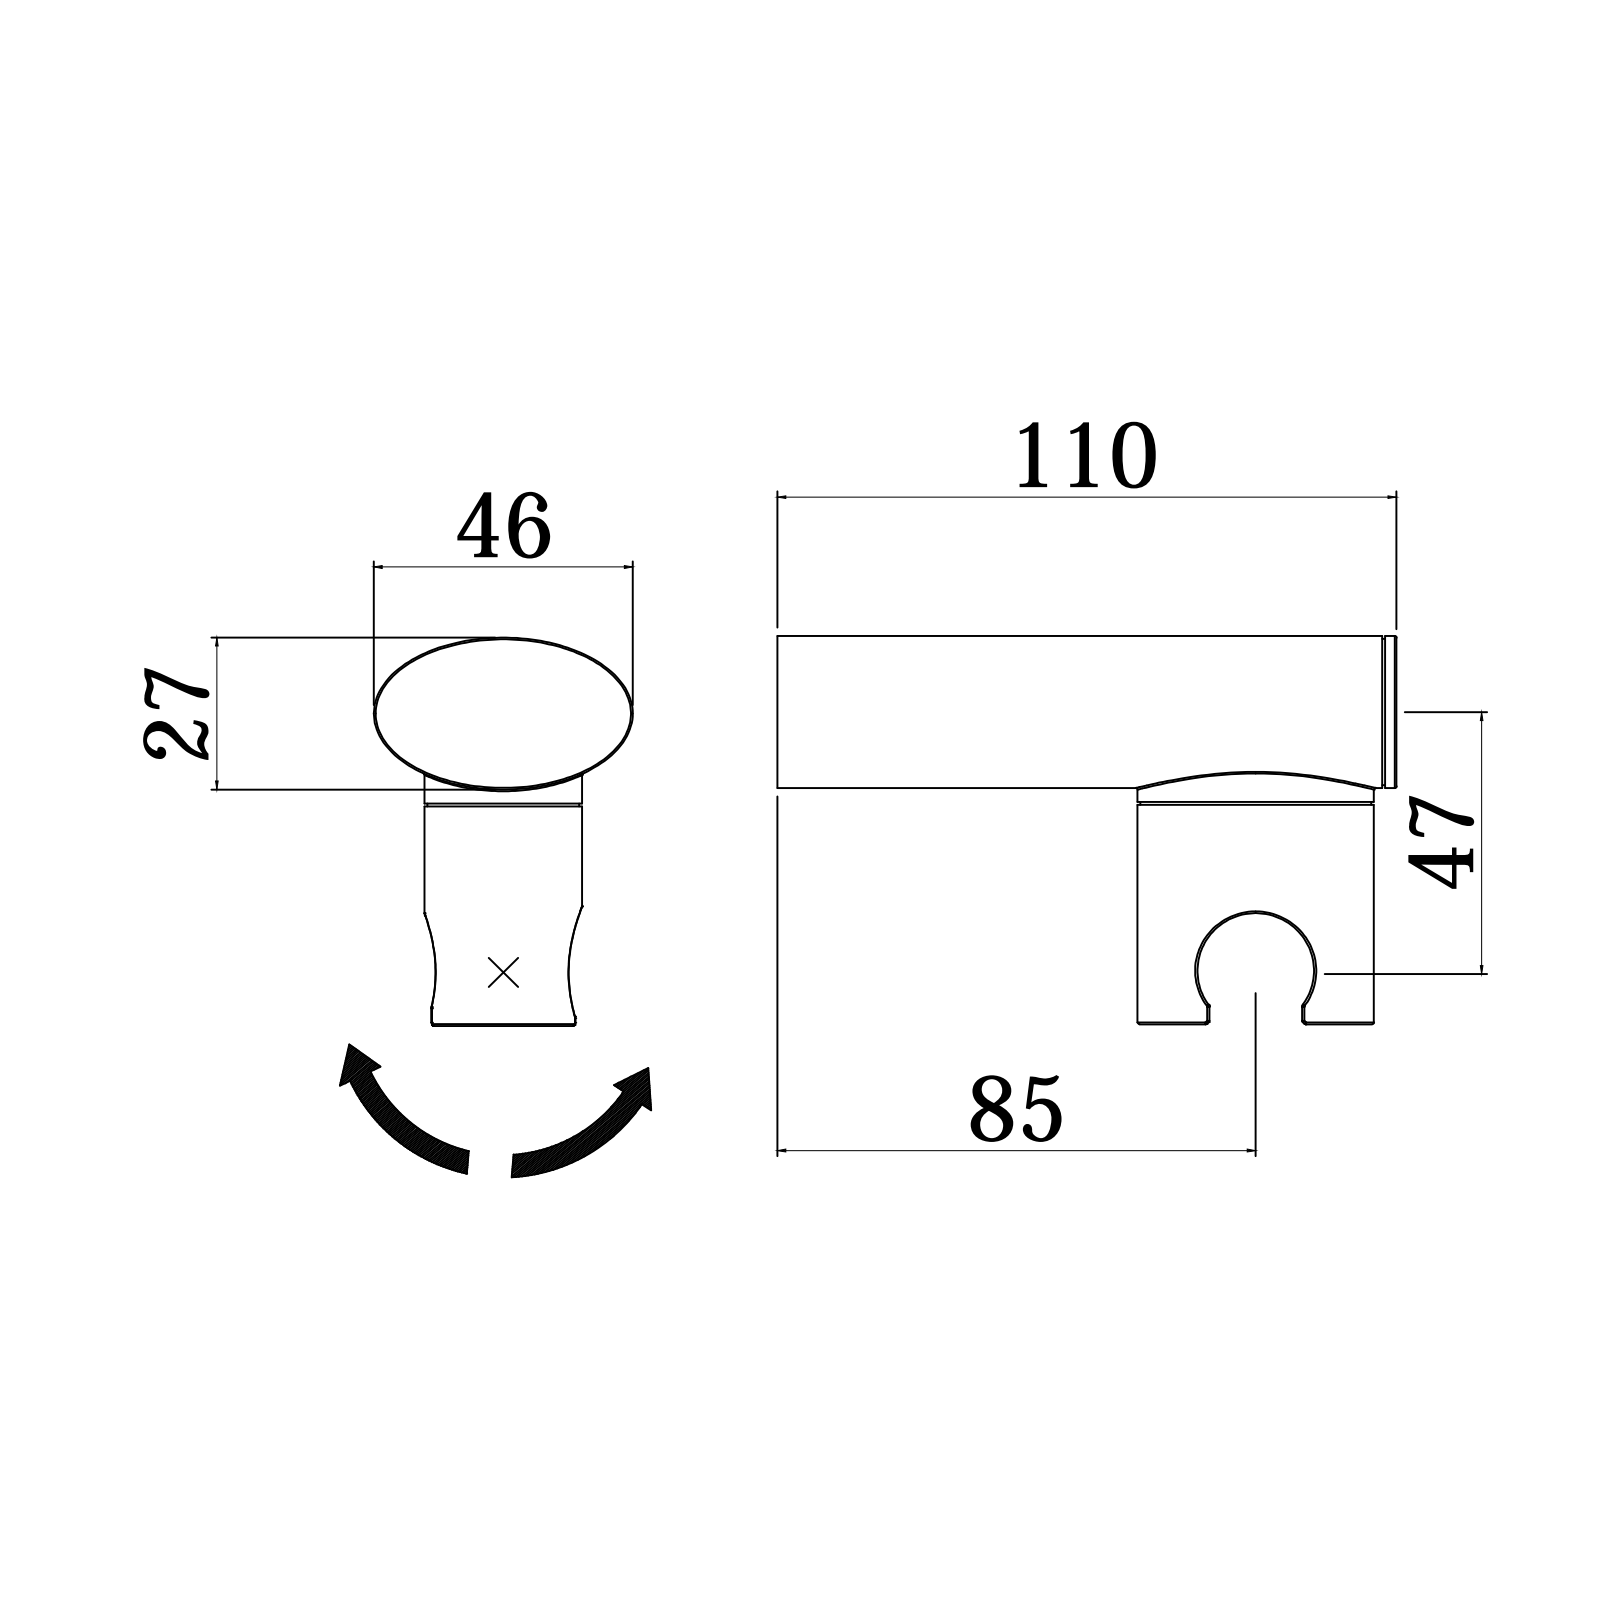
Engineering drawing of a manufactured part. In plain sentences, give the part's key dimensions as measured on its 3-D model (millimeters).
The part is named "4071431CR_CORPO; 4071431CR_PLACCHETTA; 4071431CR_GANCIO; 4071431CR_VITE (+1 more)". Its 3-D file was written by "CREO PARAMETRIC BY PTC INC, 2020044 (CONFIG_CONTROL_DESIGN)". It is 2 solids with 821 faces: 225 planar, 194 cylindrical and 402 other. Overall it measures 111 by 68.91 by 46 millimeters. Its volume is 2 818 cubic millimeters and its surface area 44 492 square millimeters. Round bosses or shafts: 1 of diameter 7.4, 1 of diameter 3.9, 1 of diameter 2.8. Partial cylindrical surfaces (rounded edges, fillets, slot ends): 32 of radius 0.3, 14 of radius 1, 12 of radius 0.5, 8 of radius 4, 6 of radius 0.8, 2 of radius 0.8, 2 of radius 2. The main face-to-face distances are 108, 2.5, 105.5, 2.8, 2.9, 0.4, 100, 5.5, 8, 1.65.
